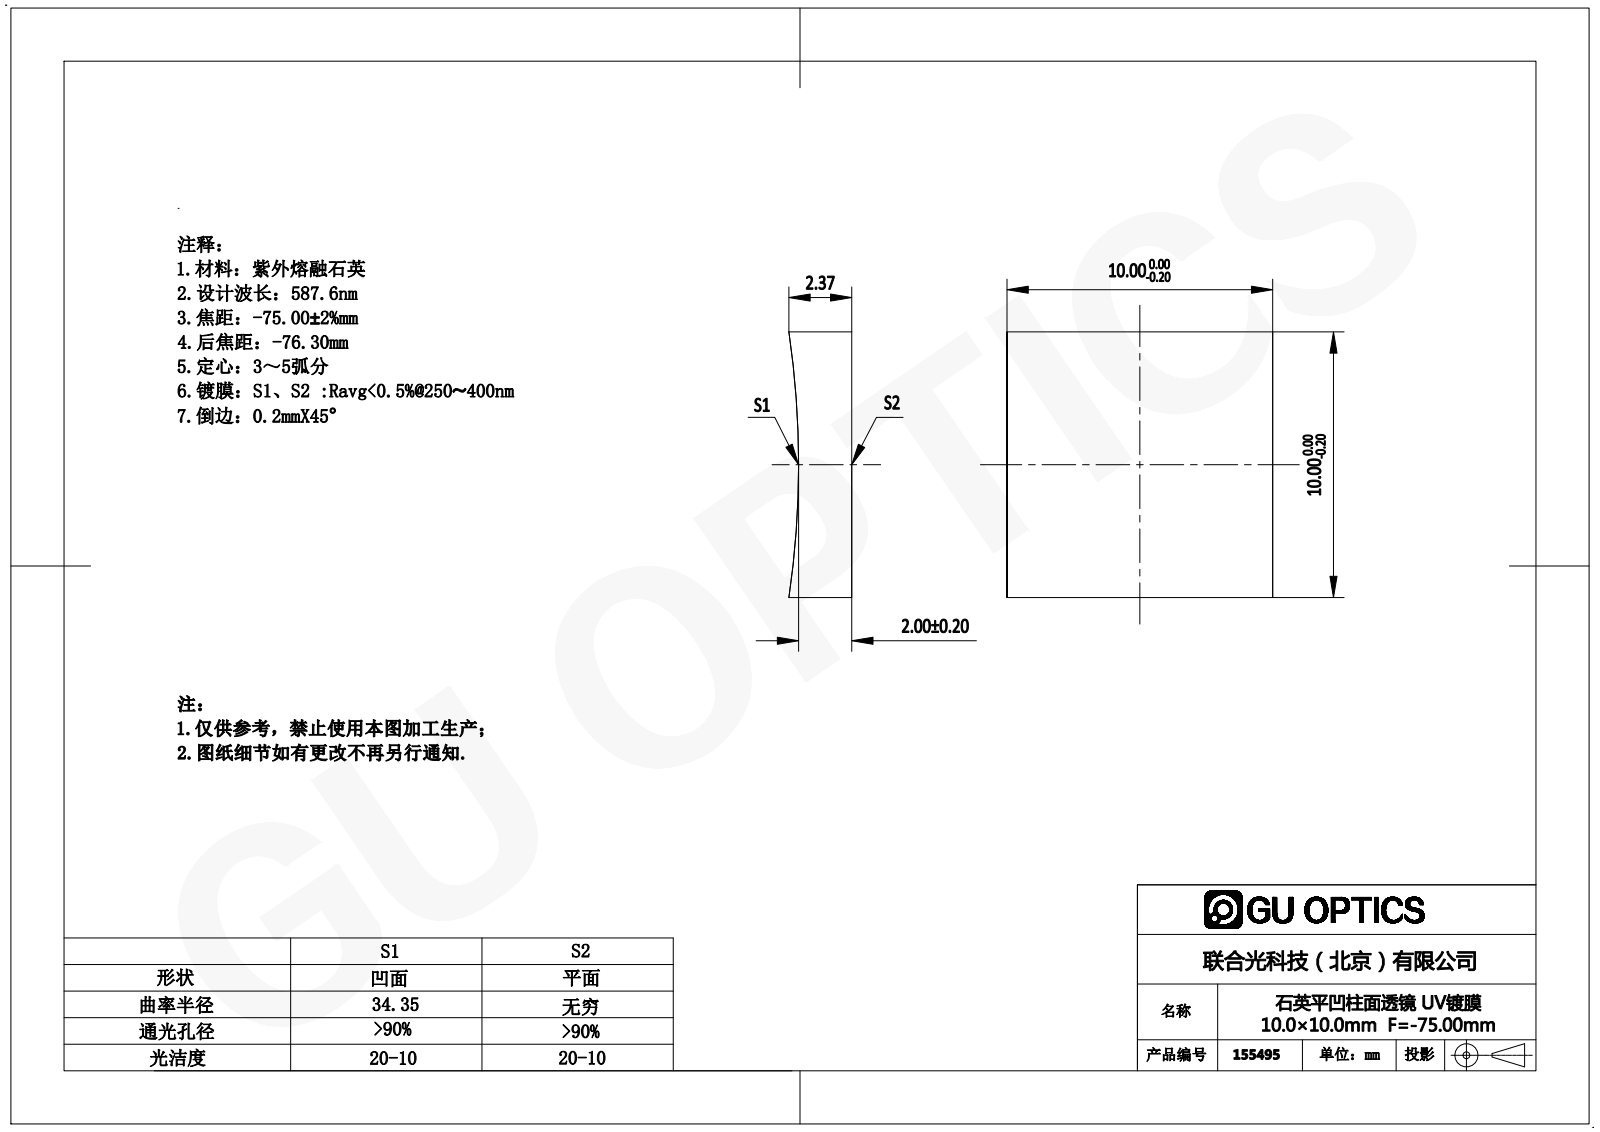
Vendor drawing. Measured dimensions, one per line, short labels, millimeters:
name: 155469
written by: SolidWorks 2016 (AUTOMOTIVE_DESIGN)
unit: mm
bodies: 1 solid, 6 faces (5 planar, 1 cylindrical, 0 other)
size: 10 × 10 × 2.37
volume: 212 mm³; area: 290 mm²
rounds: 1× R34.35
face distances: 10
